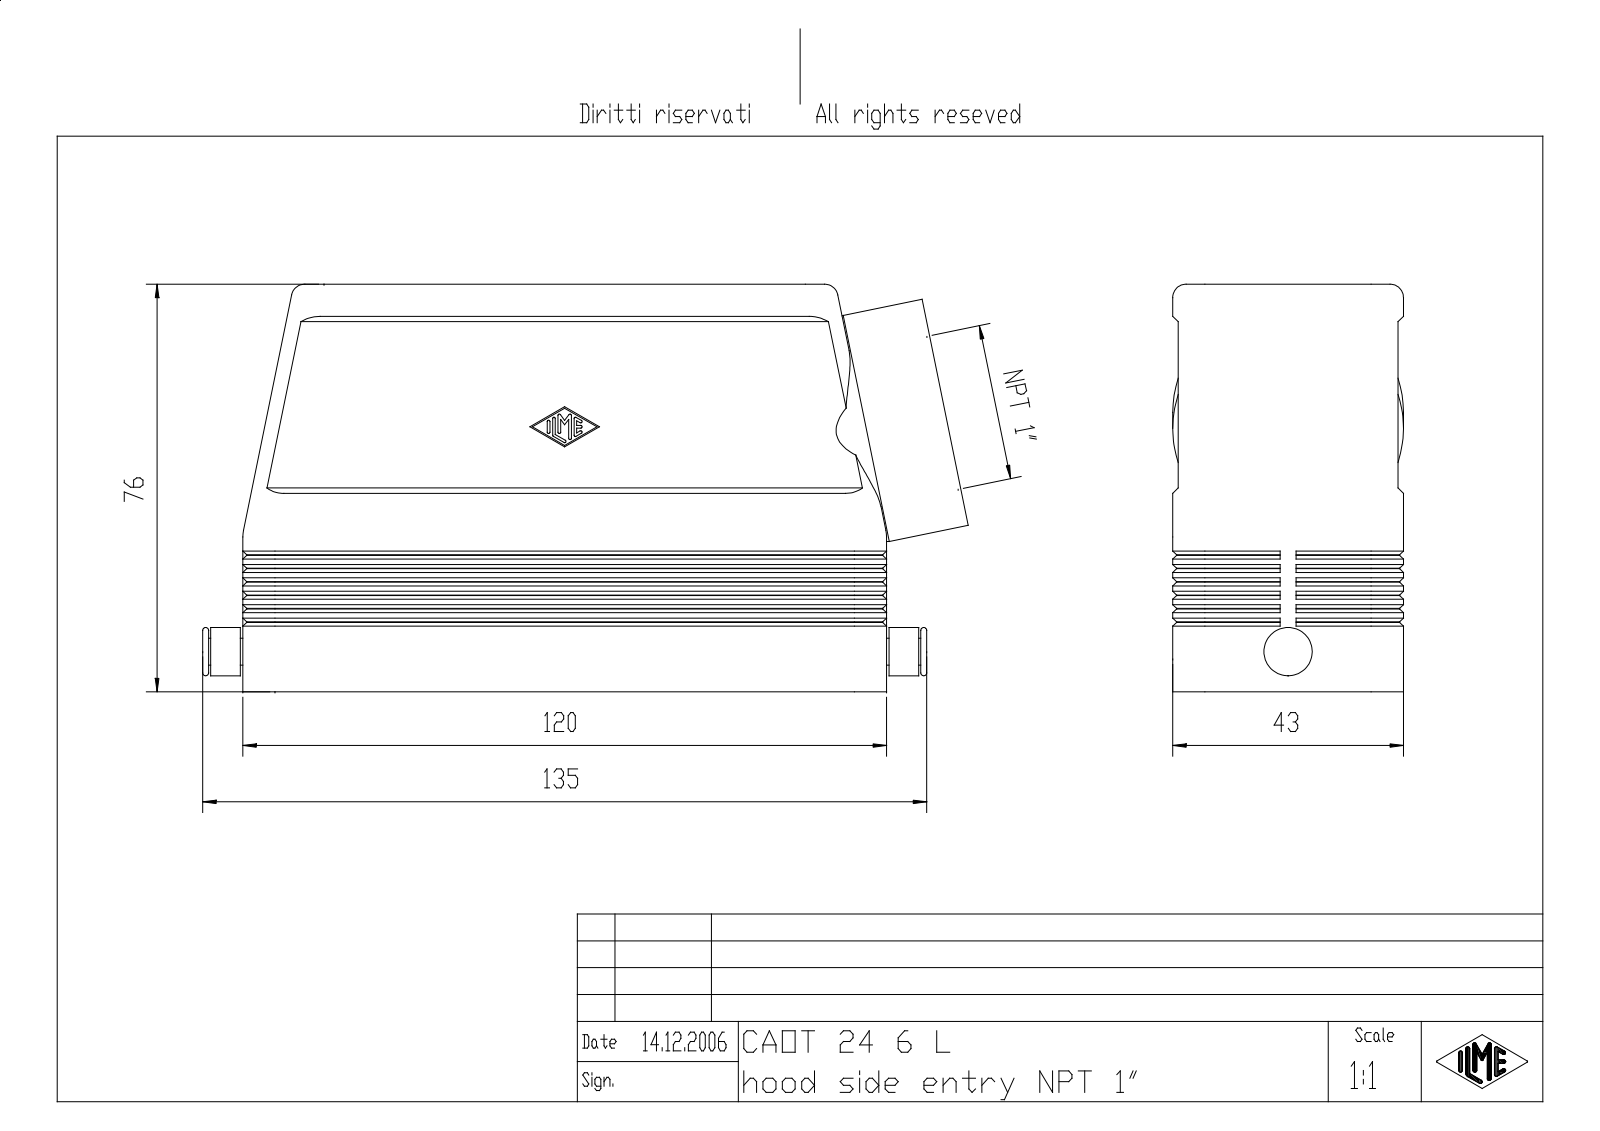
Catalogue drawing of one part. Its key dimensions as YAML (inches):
part_name: "MSBO8825"
step_written_by: "Creo Elements/Direct Modeling 18.0B 02-Dec-2011 (C) Parametric Technology GmbH (AUTOMOTIVE_DESIGN)"
units: inches
bodies: {solids: 1, faces: 425, planar: 232, cylindrical: 119, other: 74}
overall_size: [5.62, 2.992, 1.693]
volume: 5.769
surface_area: 89.86
round_holes:
  - {diameter: 0.157, count: 4}
  - {diameter: 0.097, count: 3}
  - {diameter: 0.097, count: 1}
round_bosses_or_shafts:
  - {diameter: 1.693, count: 1}
  - {diameter: 0.354, count: 1}
  - {diameter: 0.197, count: 1}
partial_cylinders:
  - {radius: 0.01, count: 14}
  - {radius: 0.236, count: 12}
  - {radius: 0.079, count: 4}
  - {radius: 0.098, count: 4}
  - {radius: 0.118, count: 4}
  - {radius: 0.209, count: 4}
face_to_face_distances: [0.118, 1.457, 1.575, 0.079, 0.039, 1.654, 1.535, 1.693, 1.614, 0.354]
hole_center_spacings: [1.063, 4.094, 4.23]
